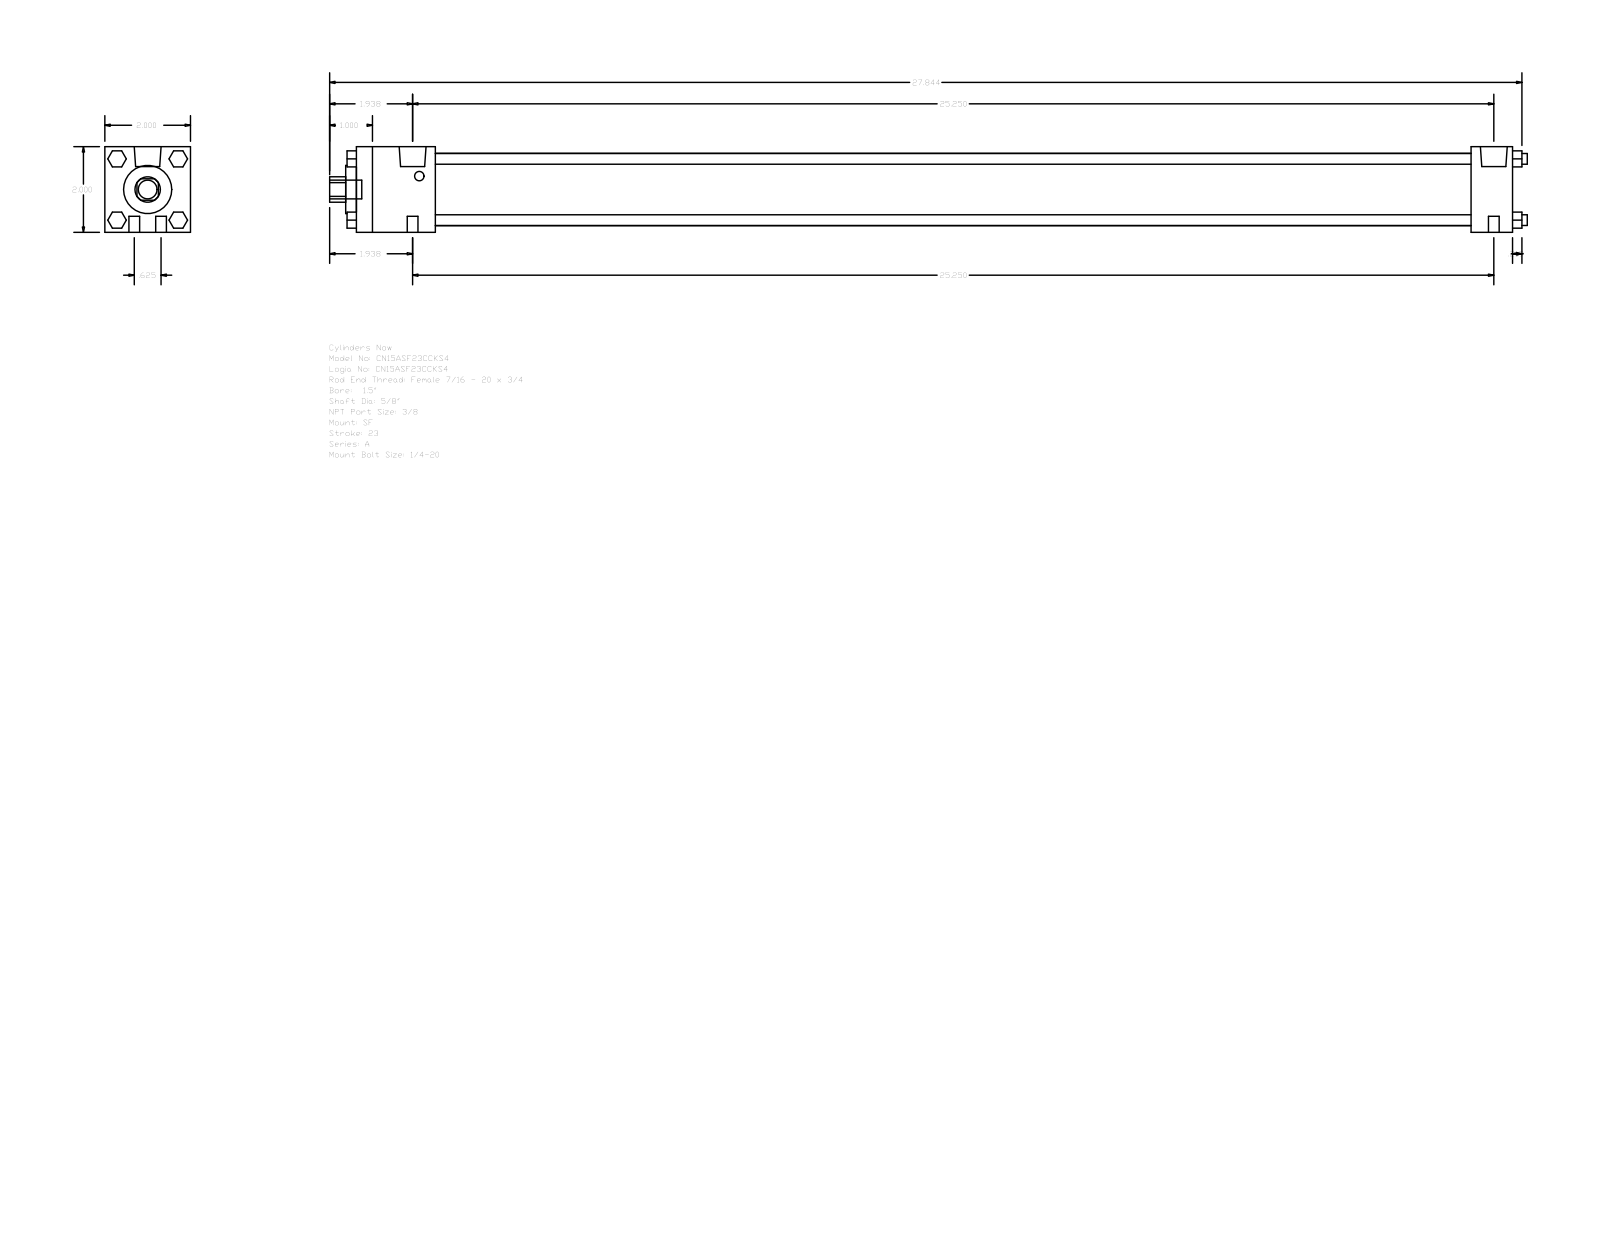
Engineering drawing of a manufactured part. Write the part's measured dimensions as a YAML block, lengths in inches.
part_name: "A_SF__0150_0.625"
step_written_by: "GSSL Pune (CONFIG_CONTROL_DESIGN)"
units: inches
bodies: {solids: 0, faces: 124, planar: 94, cylindrical: 30, other: 0}
overall_size: [27.969, 2, 2]
round_holes:
  - {diameter: 0.625, count: 1}
  - {diameter: 1.125, count: 1}
  - {diameter: 1.69, count: 1}
round_bosses_or_shafts:
  - {diameter: 0.25, count: 8}
  - {diameter: 0.627, count: 2}
  - {diameter: 0.219, count: 2}
  - {diameter: 0.437, count: 1}
partial_cylinders:
  - {radius: 0.297, count: 1}
face_to_face_distances: [2, 27, 1.844, 26.031, 24.187, 25.156, 0.969, 0.375, 0.25, 2.094]
